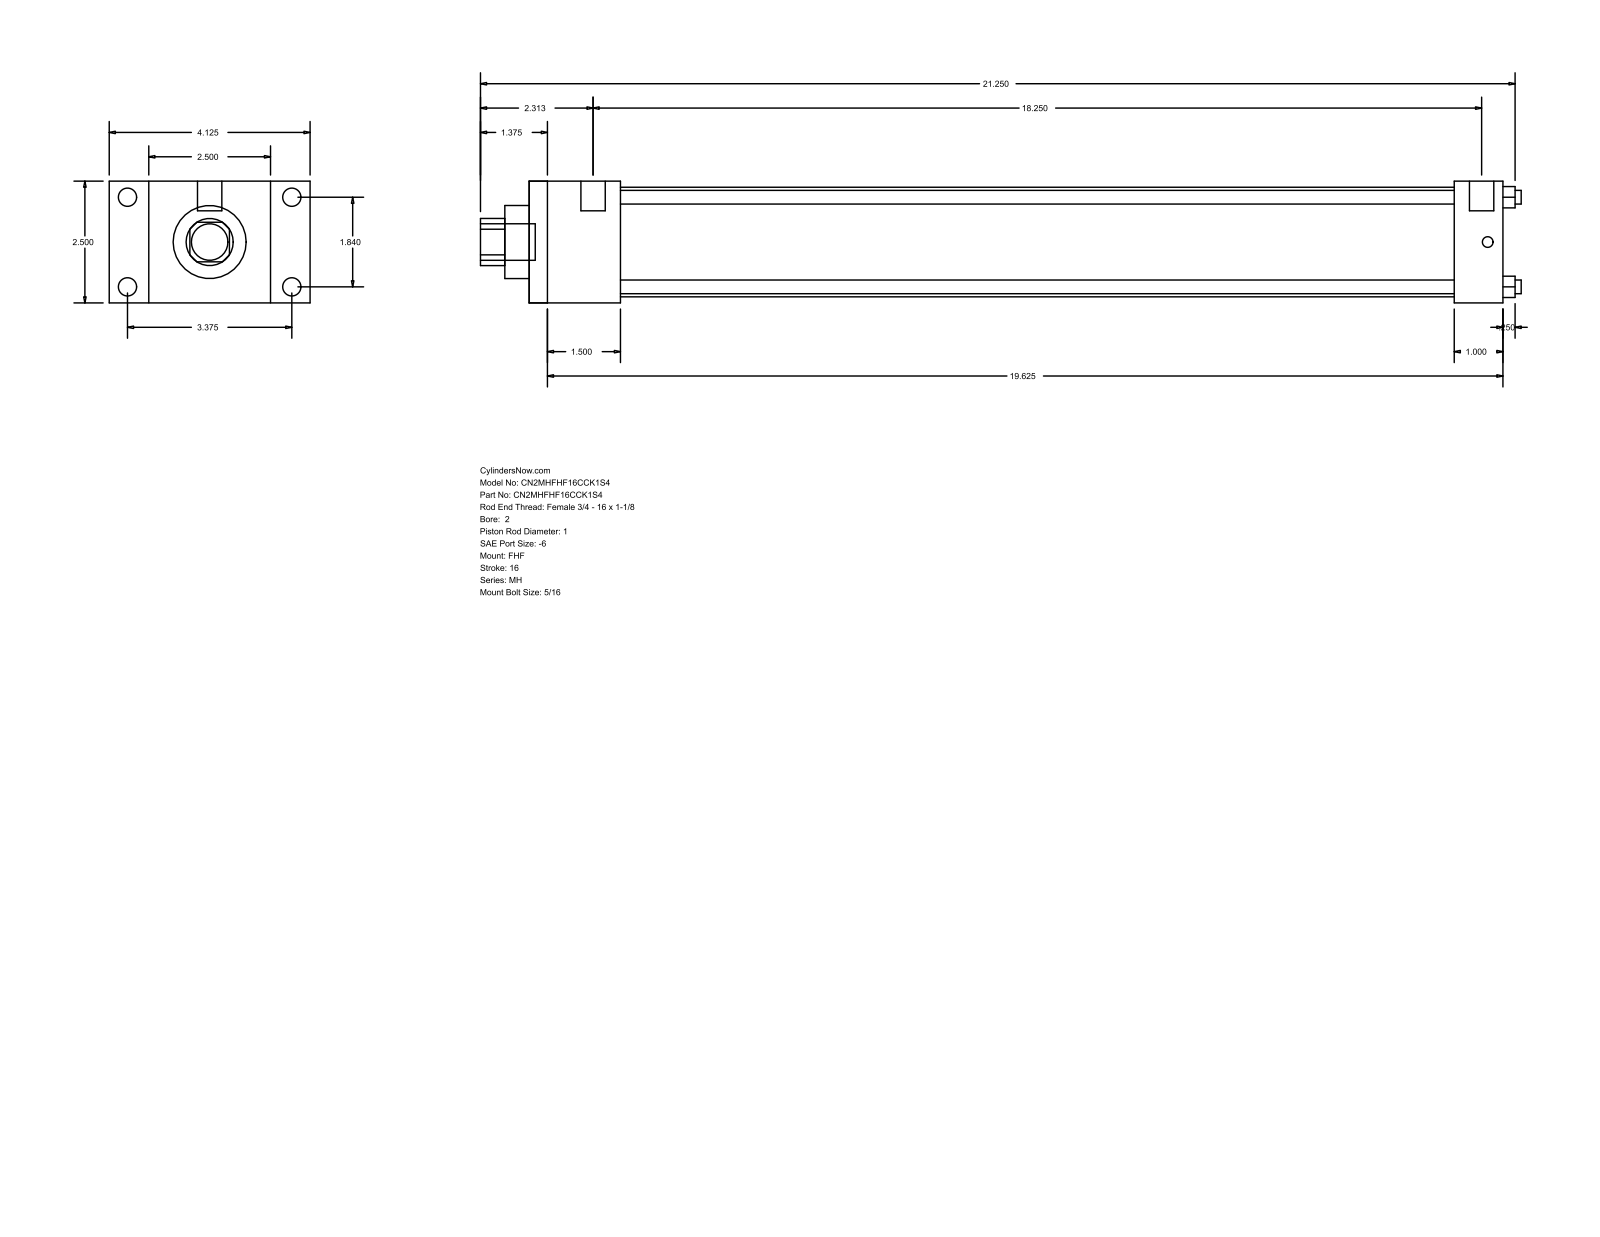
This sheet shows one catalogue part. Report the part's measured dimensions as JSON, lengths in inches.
{"part_name": "MH_FHF__0200_1", "step_written_by": "GSSL Pune (CONFIG_CONTROL_DESIGN)", "units": "inches", "bodies": {"solids": 0, "faces": 88, "planar": 60, "cylindrical": 28, "other": 0}, "overall_size": [21.375, 4.125, 2.5], "round_holes": [[0.281, 4], [1, 1], [1.5, 1], [2.25, 1]], "round_bosses_or_shafts": [[0.375, 4], [0.219, 4], [0.5, 2], [0.75, 1]], "partial_cylinders_radius": [[0.484, 1]], "face_to_face_distances": [2.5, 20, 1.875, 18.125, 0.813, 3.313, 4.125, 1, 19, 17.125], "hole_center_spacings": [1.301, 1.84, 2.602]}
